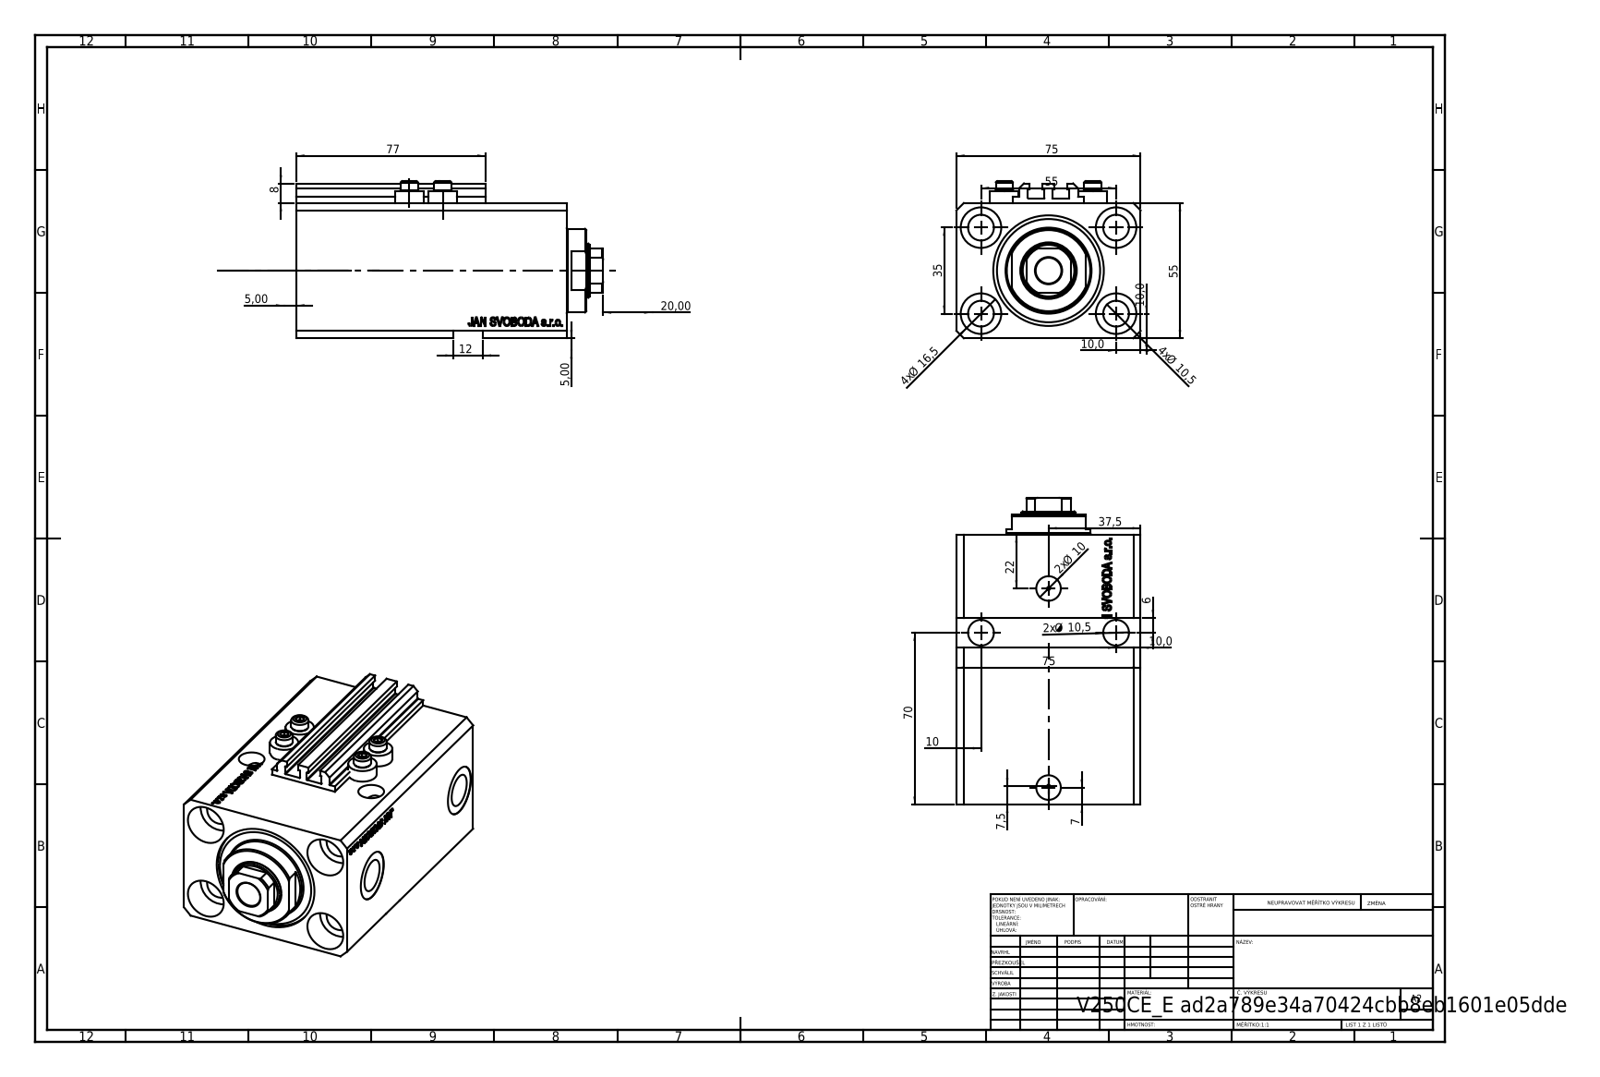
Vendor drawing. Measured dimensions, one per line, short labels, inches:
name: ALLEN BOLT V250CE; V250CE_VC_E; V250CE_C_VCP; V250CE_E_Body
written by: SolidWorks 2019 (CONFIG_CONTROL_DESIGN)
unit: in
bodies: 8 solids, 1064 faces (514 planar, 126 cylindrical, 424 other)
size: 4.917 × 2.953 × 2.52
volume: 23.66 in³; area: 149.9 in²
holes: 7× ⌀0.413, 4× ⌀0.049, 4× ⌀0.157, 4× ⌀0.65, 2× ⌀0.394, 2× ⌀0.518, 2× ⌀0.787, 1× ⌀0.866, 1× ⌀1.26, 1× ⌀1.772
bosses: 4× ⌀0.457, 4× ⌀0.276, 1× ⌀1.339
rounds: 10× R0.008, 1× R0.413
face distances: 2.165, 2.953, 4.331, 3.264, 1.067, 0.118, 0.39, 2.874, 3.941, 2.244
hole spacings: 1.283, 2.165, 0.535, 0.555, 1.016, 1.294, 1.324, 1.378
